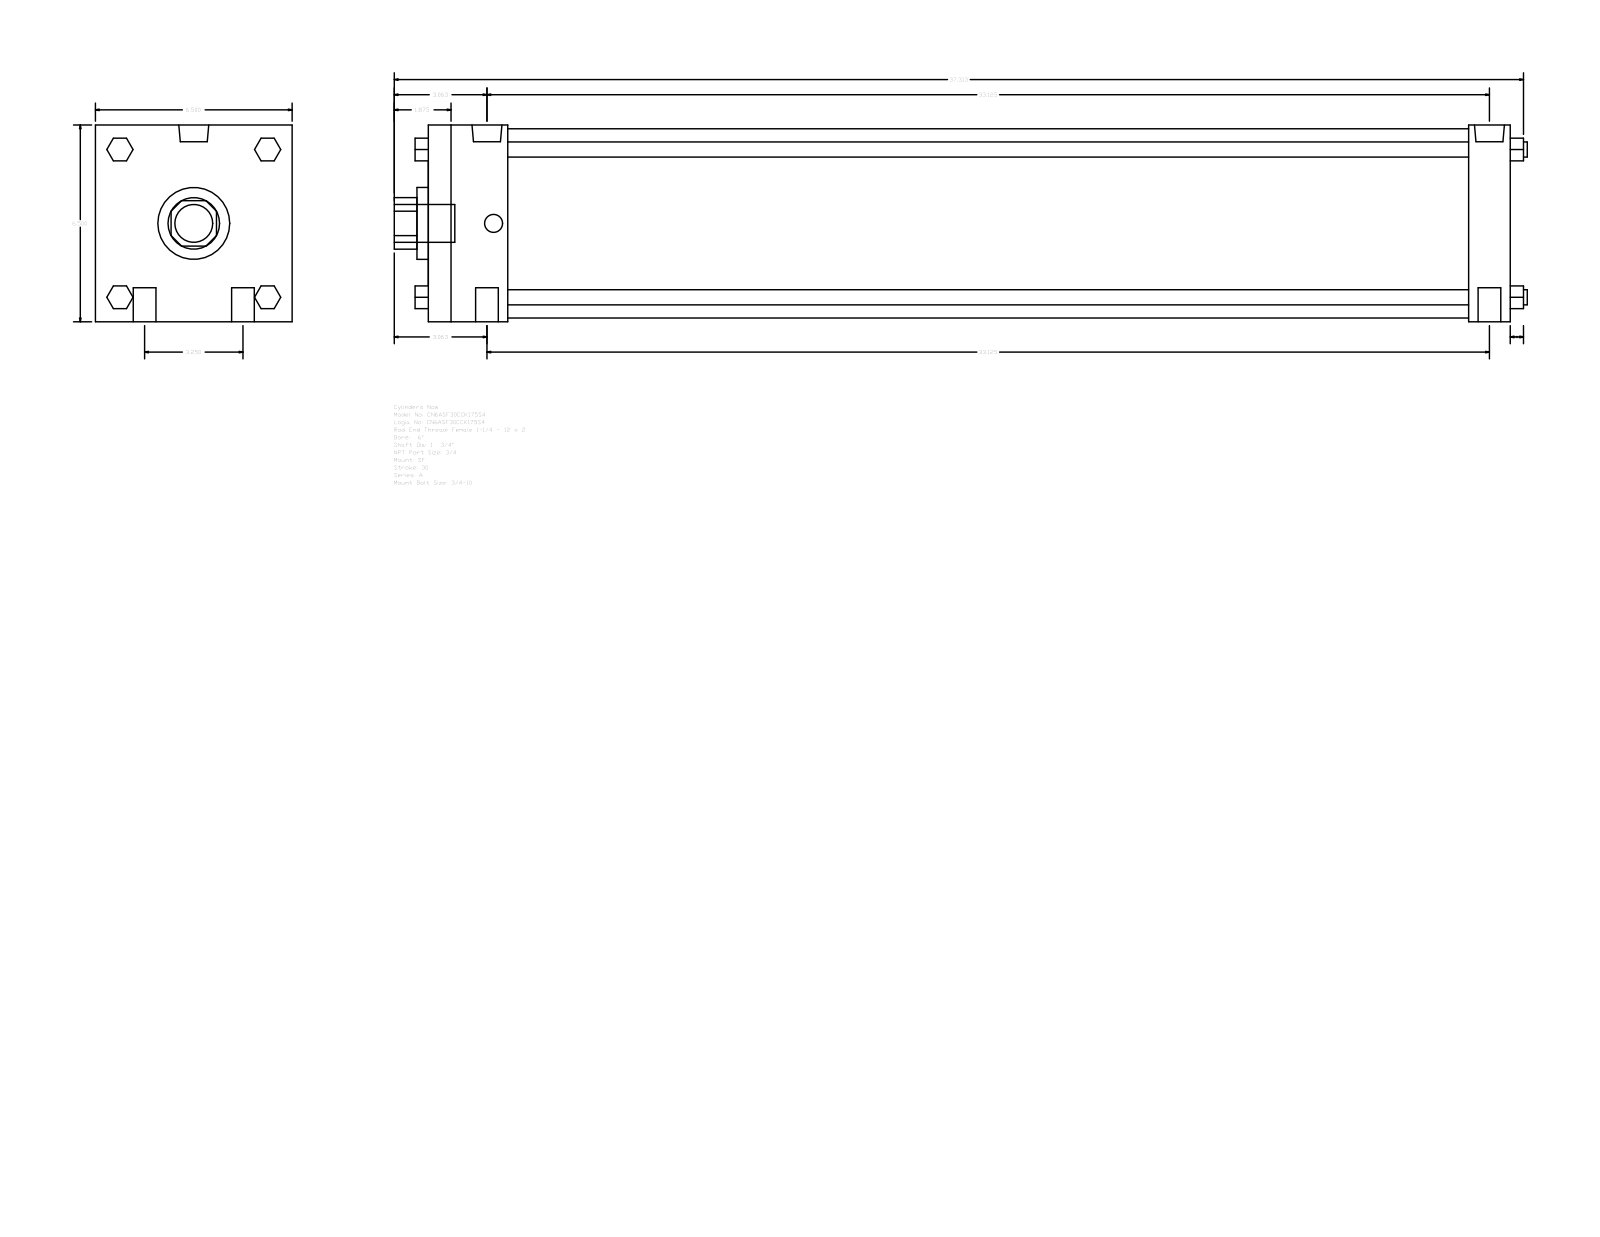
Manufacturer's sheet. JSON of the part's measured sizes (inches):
{"part_name": "A_SF__0600_1.75", "step_written_by": "GSSL Pune (CONFIG_CONTROL_DESIGN)", "units": "inches", "bodies": {"solids": 0, "faces": 124, "planar": 94, "cylindrical": 30, "other": 0}, "overall_size": [37.437, 6.5, 6.5], "round_holes": [[1.75, 1], [2.375, 1], [6.25, 1]], "round_bosses_or_shafts": [[0.75, 4], [0.5, 4], [0.989, 2], [0.594, 2], [1.25, 1]], "partial_cylinders_radius": [[0.852, 1]], "face_to_face_distances": [6.5, 35.75, 1.375, 34.375, 2.625, 31.75, 33.125, 0.75, 2.44, 4.226]}
